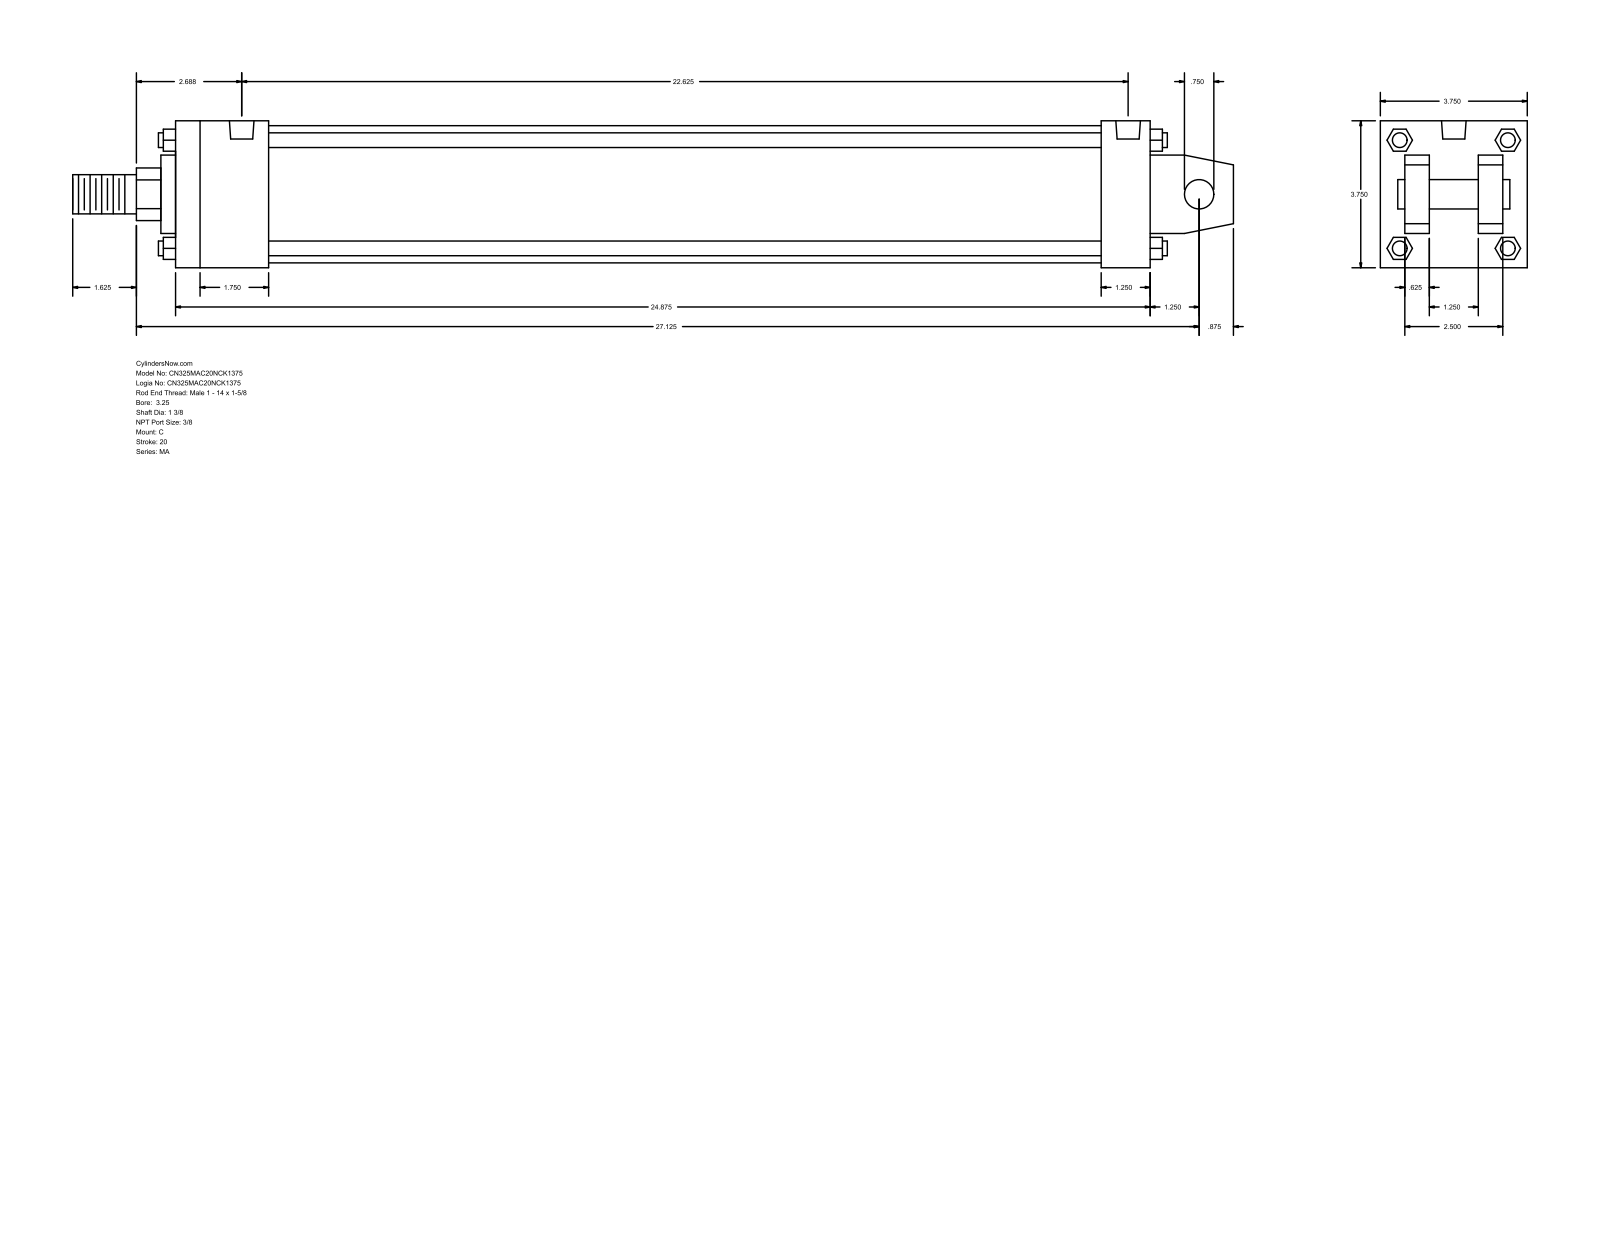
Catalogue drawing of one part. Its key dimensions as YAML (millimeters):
part_name: "MA_C__0325_1.375"
step_written_by: "GSSL Pune (CONFIG_CONTROL_DESIGN)"
units: millimeters
bodies: {solids: 0, faces: 139, planar: 108, cylindrical: 31, other: 0}
overall_size: [752.48, 95.25, 95.25]
round_holes:
  - {diameter: 11.11, count: 4}
  - {diameter: 15.93, count: 2}
round_bosses_or_shafts:
  - {diameter: 9.53, count: 4}
  - {diameter: 88.9, count: 1}
  - {diameter: 50.8, count: 1}
  - {diameter: 34.92, count: 1}
  - {diameter: 25.4, count: 1}
  - {diameter: 19.05, count: 1}
partial_cylinders:
  - {radius: 17.06, count: 1}
face_to_face_distances: [95.24, 15.87, 63.5, 631.83, 31.74, 79.37, 47.63, 600.08, 31.75, 60.32]
hole_center_spacings: [4.77, 565.14, 569.91, 574.68]
